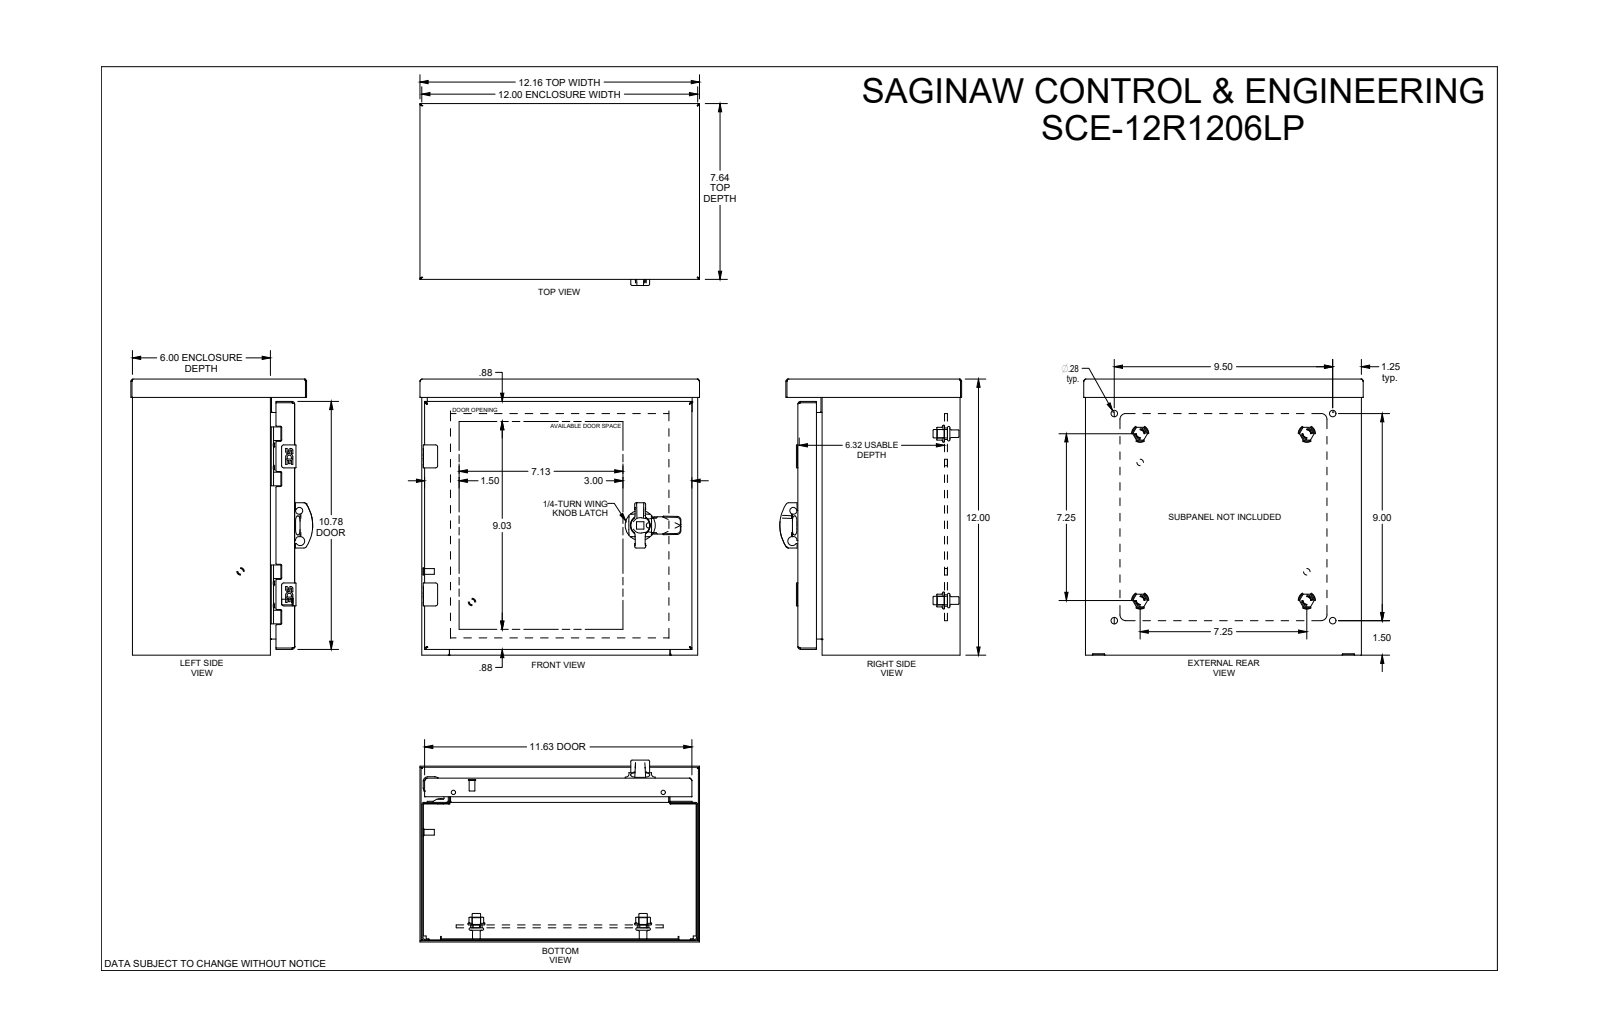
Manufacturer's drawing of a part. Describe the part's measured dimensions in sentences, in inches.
The part is named "SCE-12R1206LP". Its 3-D file was written by "SolidWorks 2019 (AUTOMOTIVE_DESIGN)". It is 39 solids with 1661 faces: 783 planar, 560 cylindrical and 318 other. Overall it measures 12.156 by 12 by 7.905 inches. Its volume is 65.77 cubic inches and its surface area 1 853 square inches. Round holes: 4 of diameter 0.172, 4 of diameter 0.205, 4 of diameter 0.244, 4 of diameter 0.266, 4 of diameter 0.281, 4 of diameter 0.367, 4 of diameter 0.375, 4 of diameter 0.5, 2 of diameter 0.04, 2 of diameter 0.188, 2 of diameter 0.218, 2 of diameter 0.281. Round bosses or shafts: 6 of diameter 0.17, 4 of diameter 0.366, 4 of diameter 0.332, 4 of diameter 0.25, 4 of diameter 0.24, 3 of diameter 0.196, 2 of diameter 0.248, 1 of diameter 1.303. Partial cylindrical surfaces (rounded edges, fillets, slot ends): 48 of radius 0.015, 32 of radius 0.01, 30 of radius 0.012, 25 of radius 0.06, 14 of radius 0.062, 12 of radius 0.02, 10 of radius 0.031, 8 of radius 0.062. The main face-to-face distances are 0.06, 11.94, 6.993, 12, 11.88, 7.053, 6.933, 5.94, 1.053, 0.125. The hole center spacings are 6, 8.85, 0.013, 0.013, 0.485, 0.493, 0.494, 0.501.
